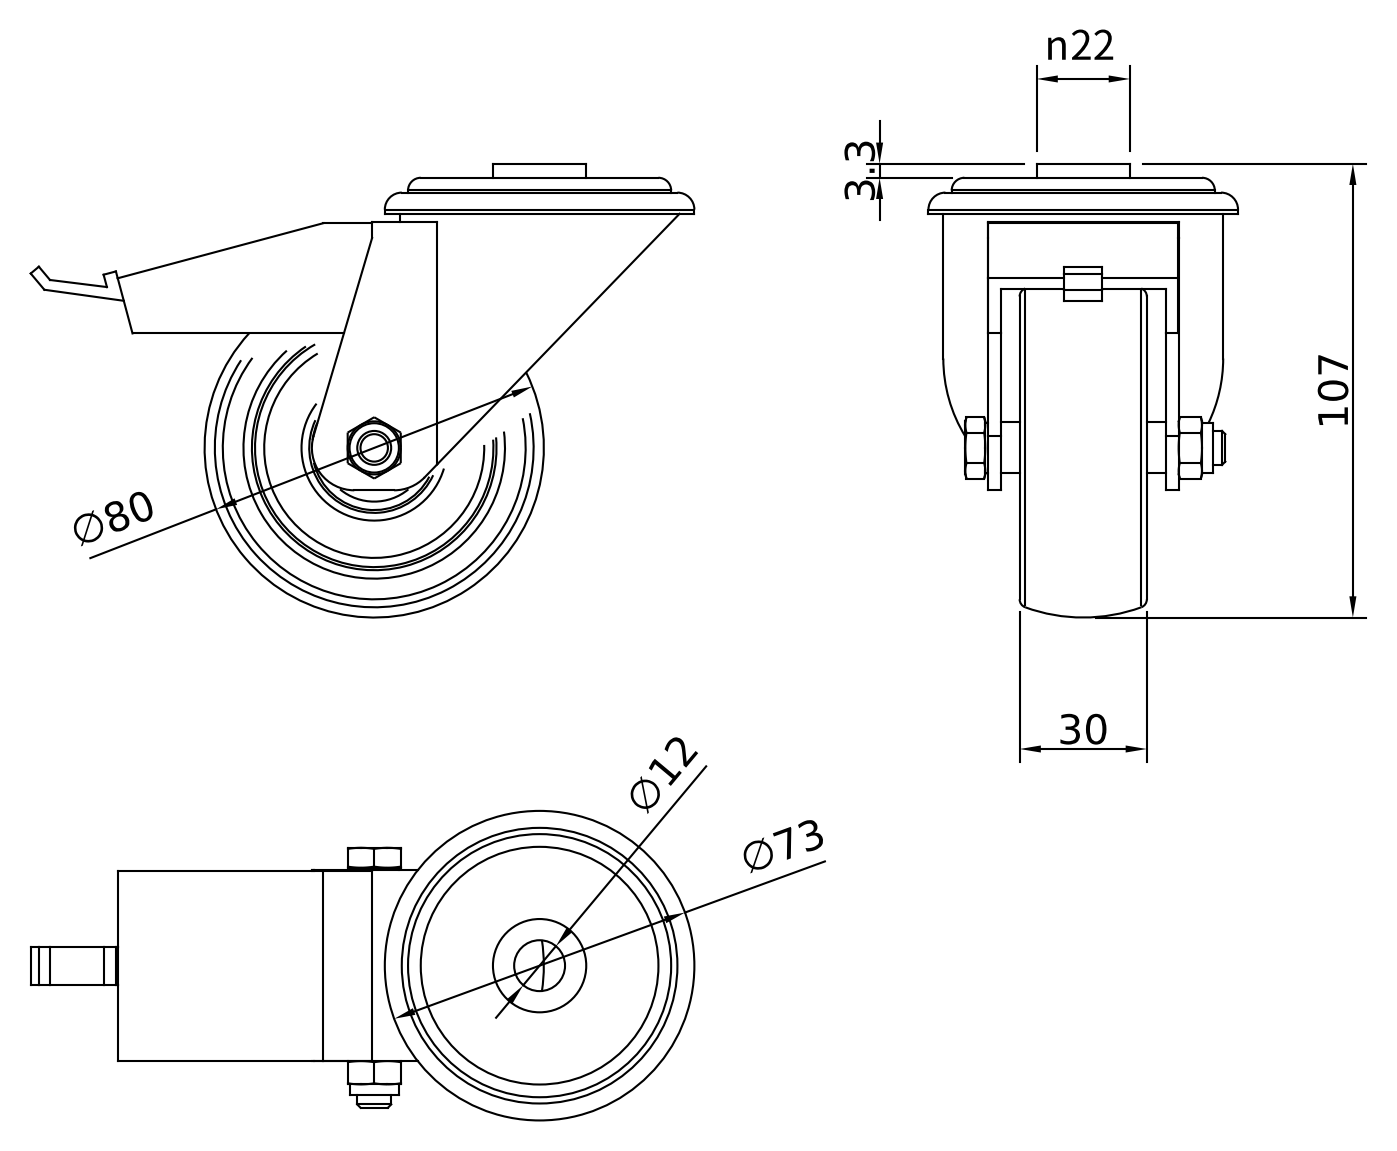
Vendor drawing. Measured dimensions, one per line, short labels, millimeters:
name: CRUST0000202; 440000025919; 440000025918; 440000025917
written by: Autodesk Inventor 2022 (AUTOMOTIVE_DESIGN)
unit: mm
bodies: 3 solids, 129 faces (65 planar, 20 cylindrical, 44 other)
size: 156.5 × 107 × 73
volume: 175 271 mm³; area: 60 194 mm²
holes: 2× ⌀12, 1× ⌀9, 1× ⌀61
bosses: 1× ⌀73, 1× ⌀66, 1× ⌀62.05, 1× ⌀22, 1× ⌀11.63, 1× ⌀8
rounds: 2× R10
face distances: 3, 42, 7.5, 37.5, 4.5, 34.5, 10.7, 39, 44.9, 2.9
